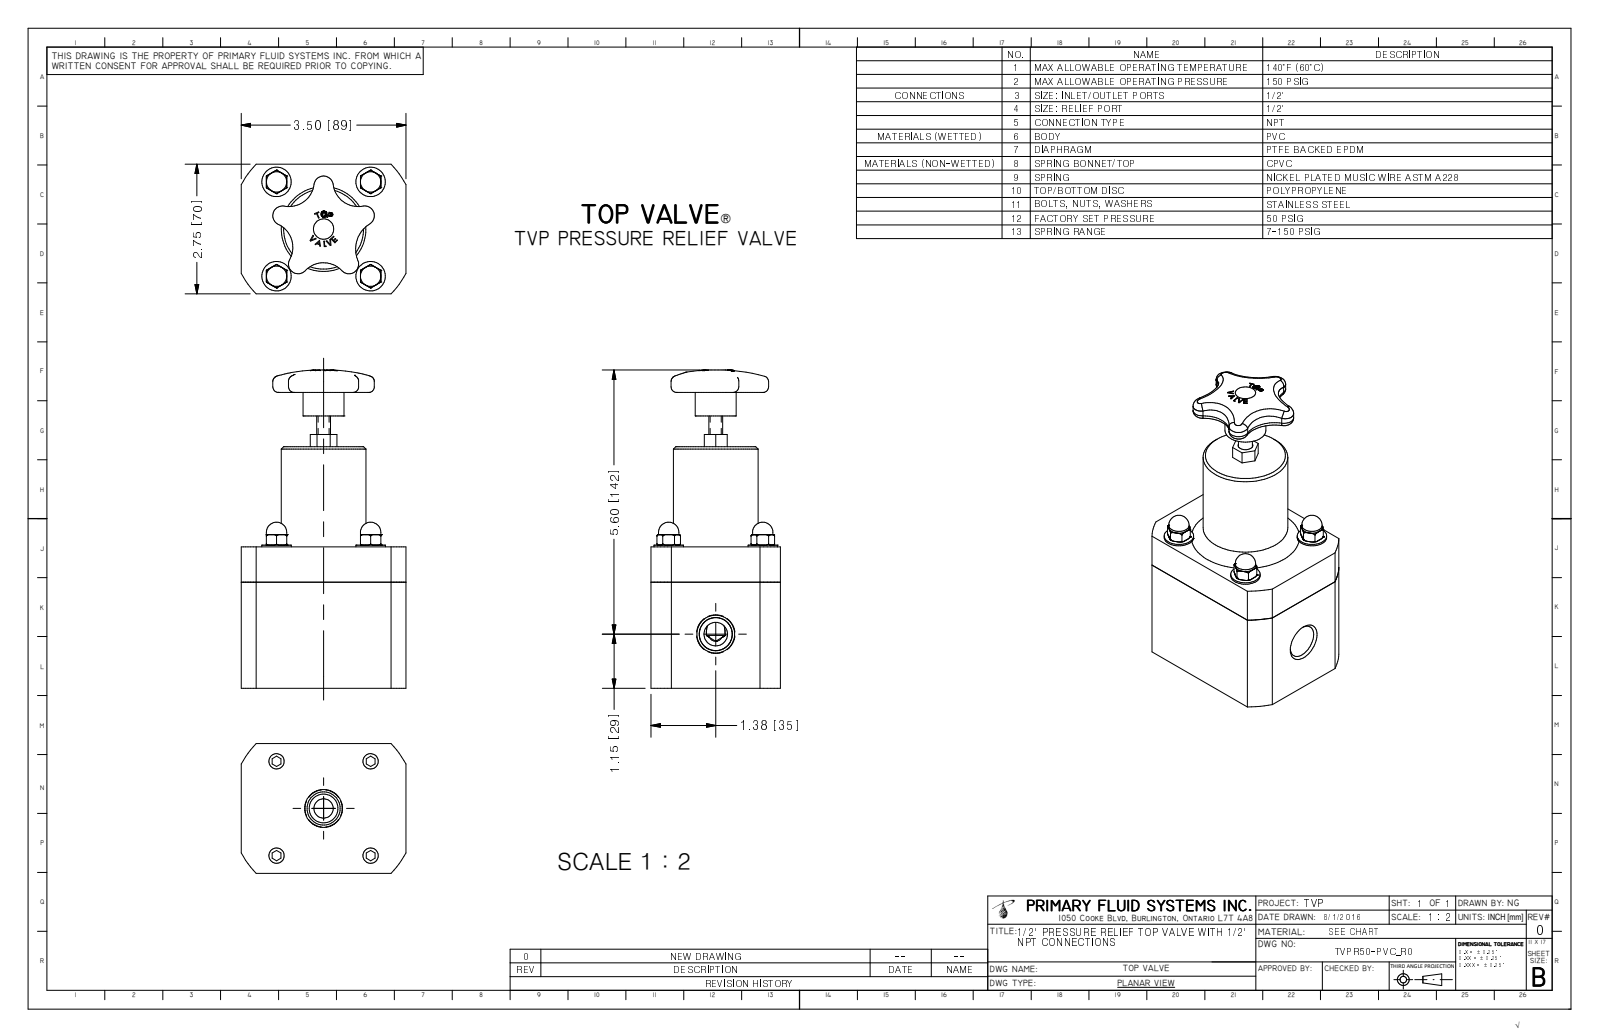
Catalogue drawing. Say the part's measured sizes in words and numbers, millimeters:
The part is named "TVPR50-PVC_R0". Its 3-D file was written by "Autodesk Inventor 2009 (AUTOMOTIVE_DESIGN)". It is 1 solid with 304 faces: 123 planar, 44 cylindrical and 137 other. Overall it measures 171.5 by 88.9 by 69.9 millimeters. Its volume is 562 100 cubic millimeters and its surface area 54 540 square millimeters. Round holes: 4 of diameter 4.4, 2 of diameter 17.9, 1 of diameter 61. Round bosses or shafts: 4 of diameter 15.9, 4 of diameter 11, 1 of diameter 60.3, 1 of diameter 45.7, 1 of diameter 22.1, 1 of diameter 7.4. Partial cylindrical surfaces (rounded edges, fillets, slot ends): 5 of radius 2.2, 5 of radius 5.2, 4 of radius 13.6, 4 of radius 16.7, 1 of radius 15.9, 1 of radius 18.9, 1 of radius 50.5. The main face-to-face distances are 69.9, 88.9, 76.2, 130.2, 54, 17.8, 71.1, 11, 77.1, 0.9. The hole center spacings are 35.9, 50.8, 71.8.
